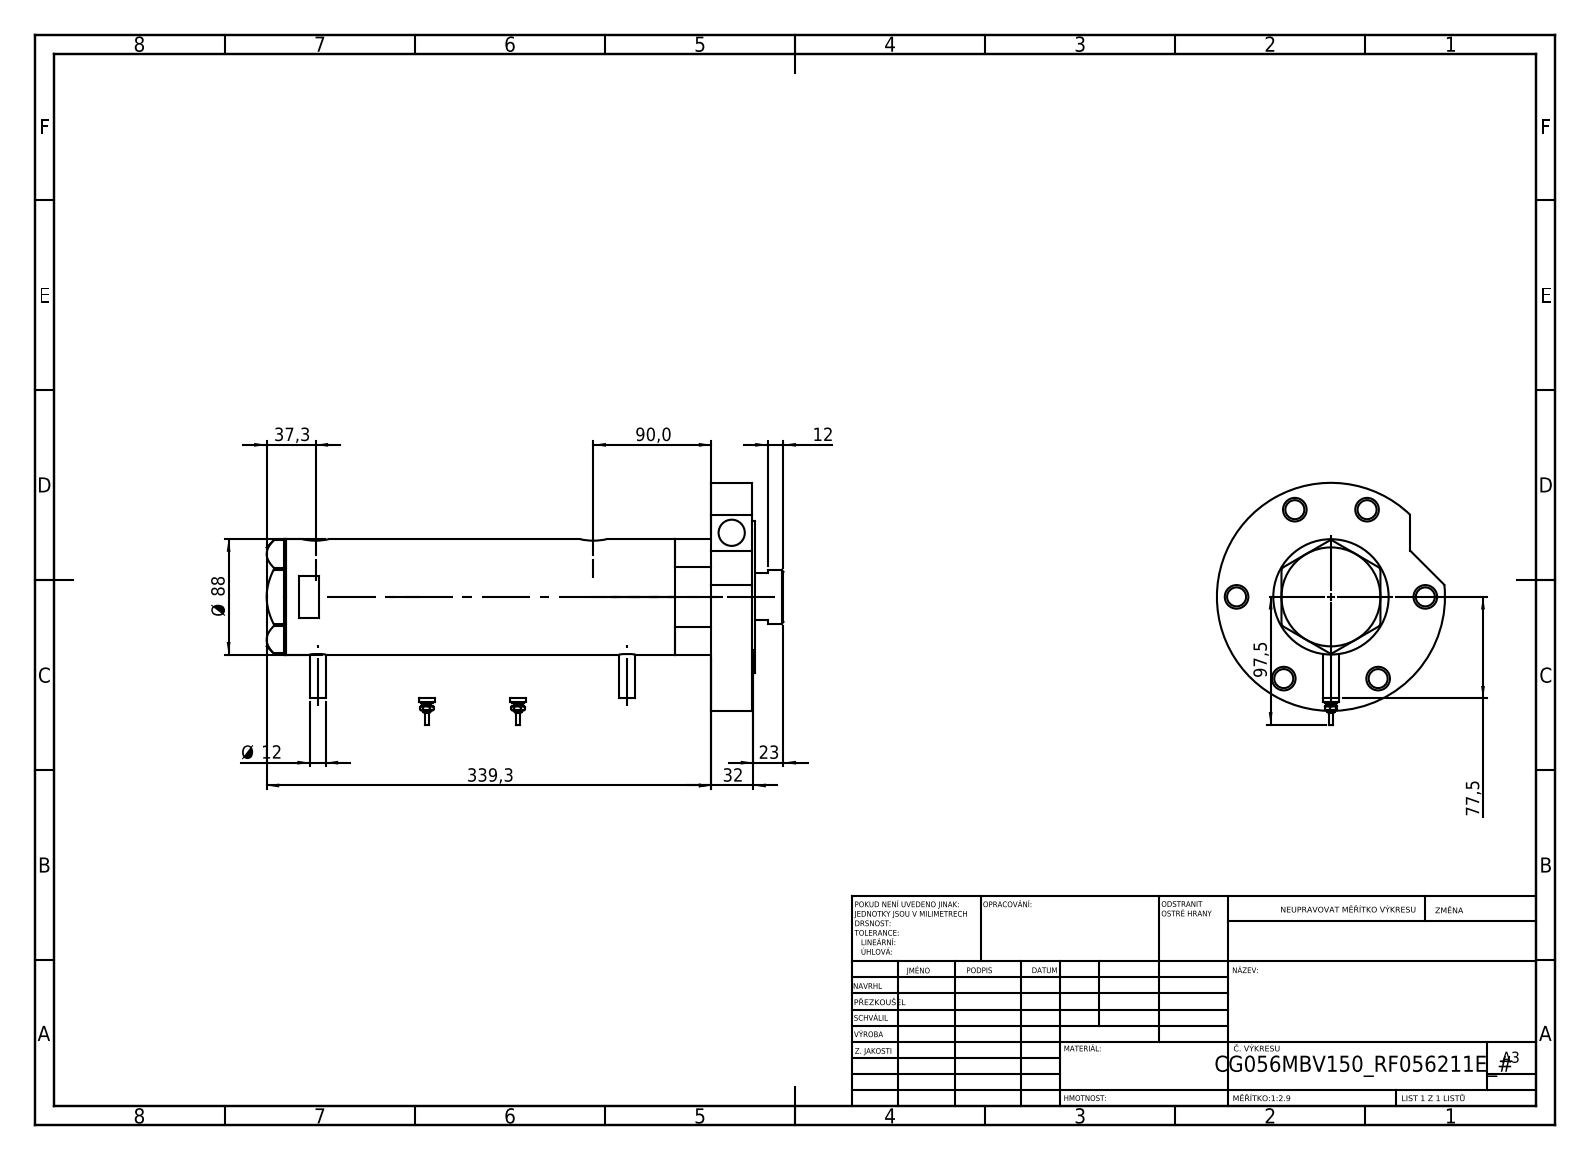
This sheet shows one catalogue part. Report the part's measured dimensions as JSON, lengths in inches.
{"part_name": "V270CG_RF211E; V270CG_MIDDLE; V270CG_BACK; V270CG_VC (+2 more)", "step_written_by": "SolidWorks 2019 (CONFIG_CONTROL_DESIGN)", "units": "inches", "bodies": {"solids": 7, "faces": 257, "planar": 91, "cylindrical": 102, "other": 64}, "overall_size": [15.524, 7.264, 6.85], "volume_in3": 156.3, "surface_area_in2": 559.1, "round_holes": [[0.571, 7], [0.709, 6], [0.787, 3], [0.492, 2], [0.518, 2], [1.654, 1], [1.713, 1], [2.205, 1], [2.362, 1], [2.953, 1], [3.15, 1]], "round_bosses_or_shafts": [[0.472, 4], [0.354, 2], [0.276, 2], [0.177, 2], [0.098, 2], [6.85, 1], [4.567, 1], [3.465, 1]], "face_to_face_distances": [1.22, 0.079, 14.067, 12.768, 13.988, 1.299, 9.228, 3.539, 4.76, 4.839], "hole_center_spacings": [2.835, 3.15, 4.714, 4.91, 5.085, 5.657, 0.067, 1.016]}
